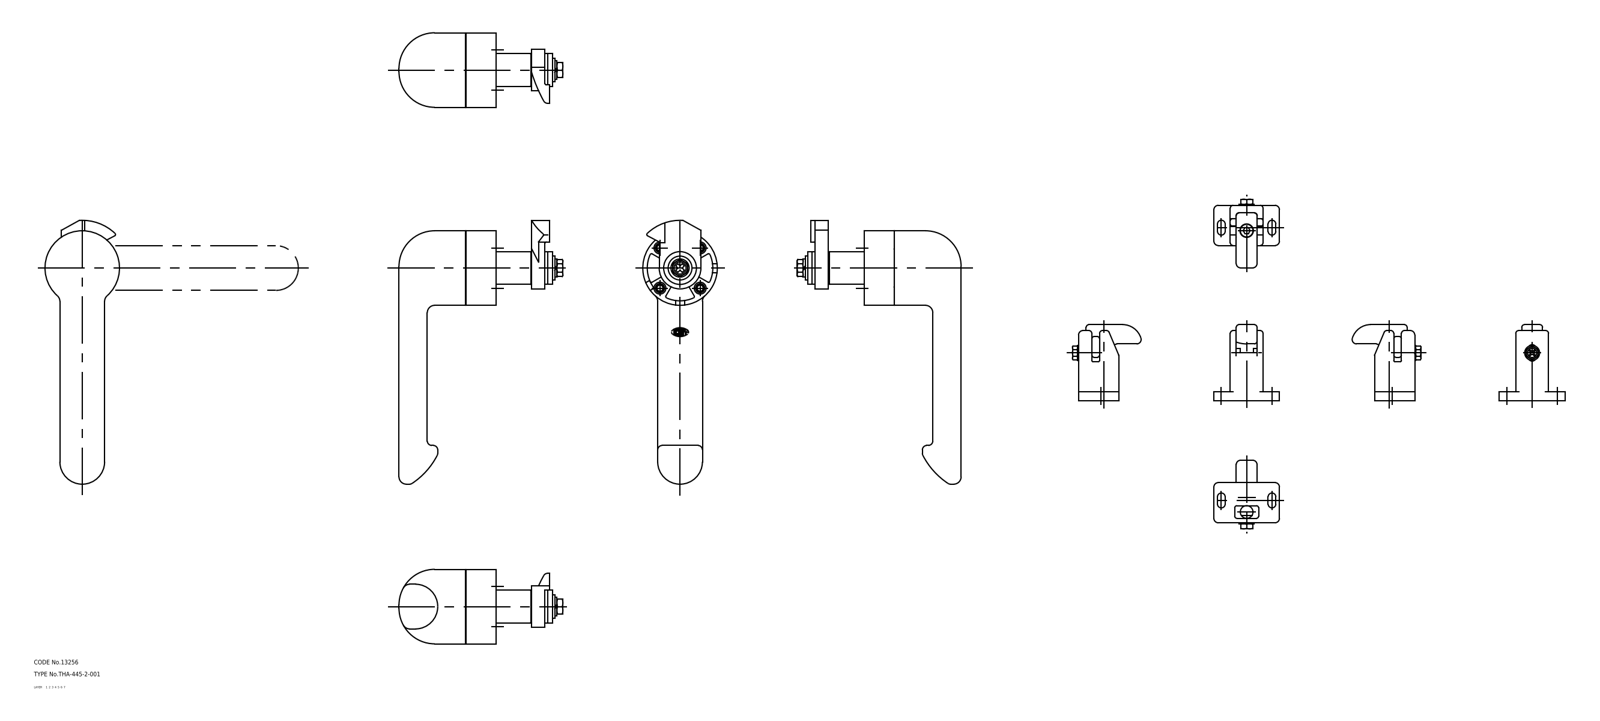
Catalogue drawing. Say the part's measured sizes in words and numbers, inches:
The part is named "67134905; 67134918; 67134931; 67134944 (+5 more)". Its 3-D file was written by "CADfix (AUTOMOTIVE_DESIGN)". It is 9 solids with 500 faces: 0 planar, 0 cylindrical and 500 other. Overall it measures 8.272 by 5 by 2.096 inches. Its volume is 13.28 cubic inches and its surface area 89.96 square inches.
